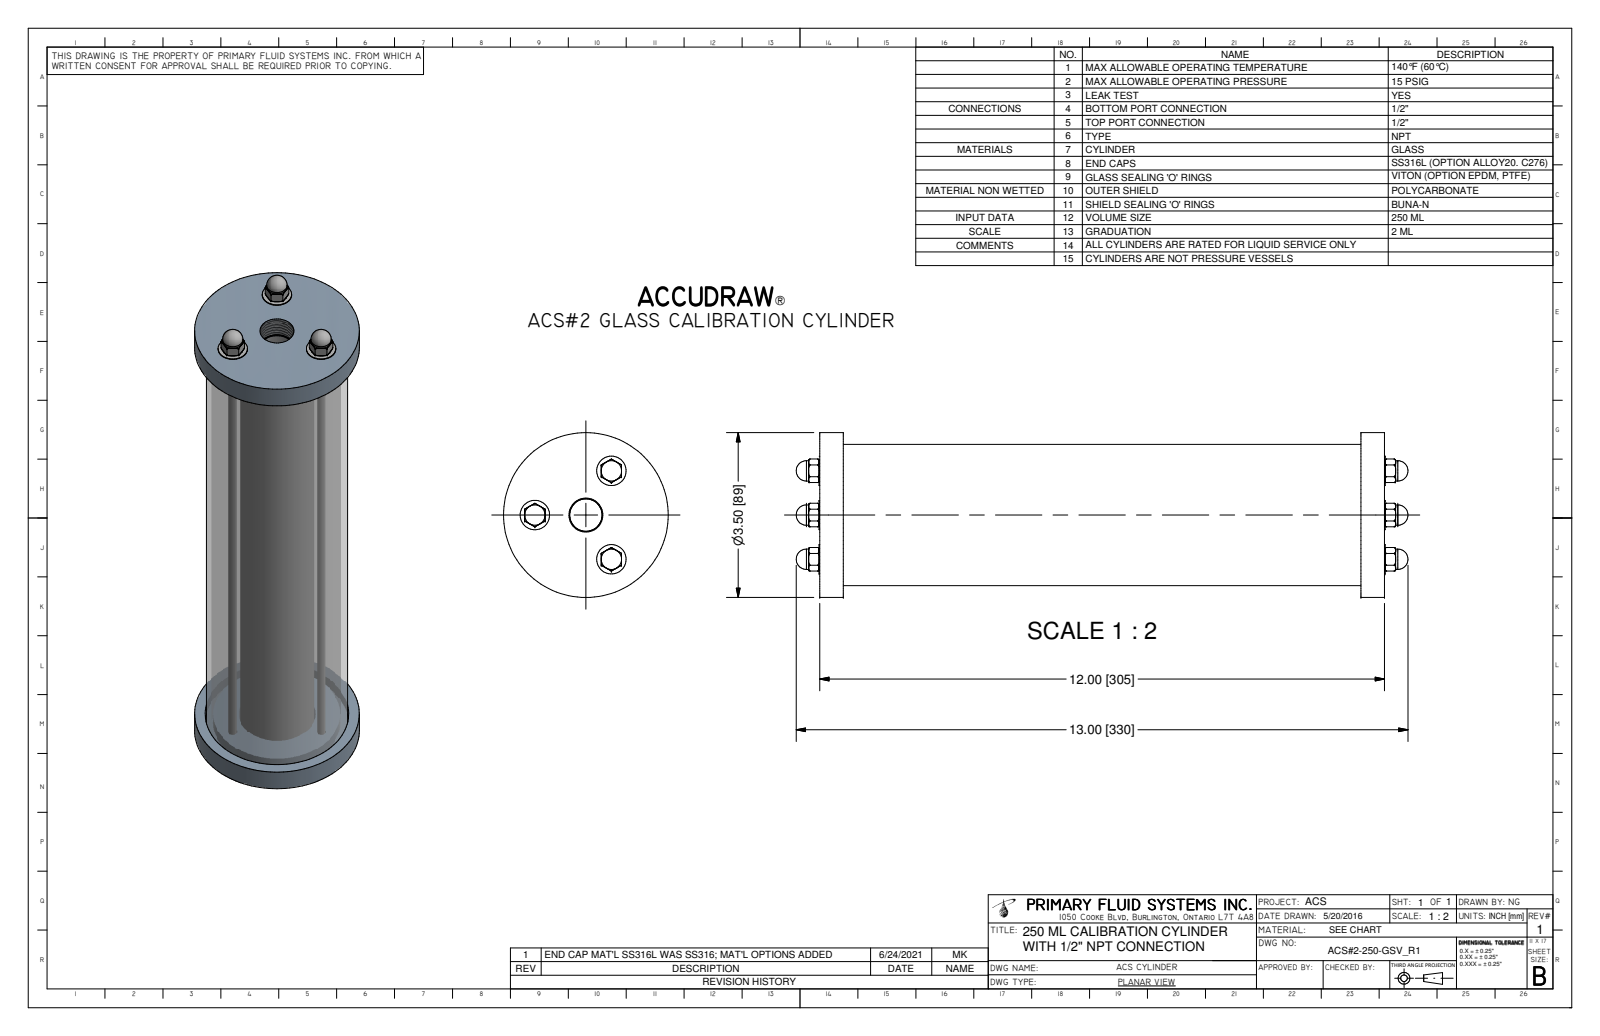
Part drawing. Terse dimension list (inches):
name: ACS#2-250-GSV_R0; ACS-3-250-METAL_R3; ACS-2-250-PC_R6; ACS-1-250-A_R0 (+3 more)
written by: Autodesk Inventor 2009 (AUTOMOTIVE_DESIGN)
unit: in
bodies: 19 solids, 429 faces (38 planar, 41 cylindrical, 350 other)
size: 13 × 3.5 × 3.5
volume: 26.68 in³; area: 425.4 in²
holes: 3× ⌀0.18, 3× ⌀0.201, 3× ⌀0.281, 1× ⌀1.417, 1× ⌀1.635, 1× ⌀2.75, 1× ⌀3.05
bosses: 3× ⌀0.625, 3× ⌀0.187, 1× ⌀3.5, 1× ⌀3, 1× ⌀2.7, 1× ⌀1.575, 1× ⌀1.365
face distances: 0.5, 11.5, 12, 11, 0.225, 11.775, 0.275, 11.275, 11.55, 0.237
hole spacings: 1.084, 1.878, 1.877
